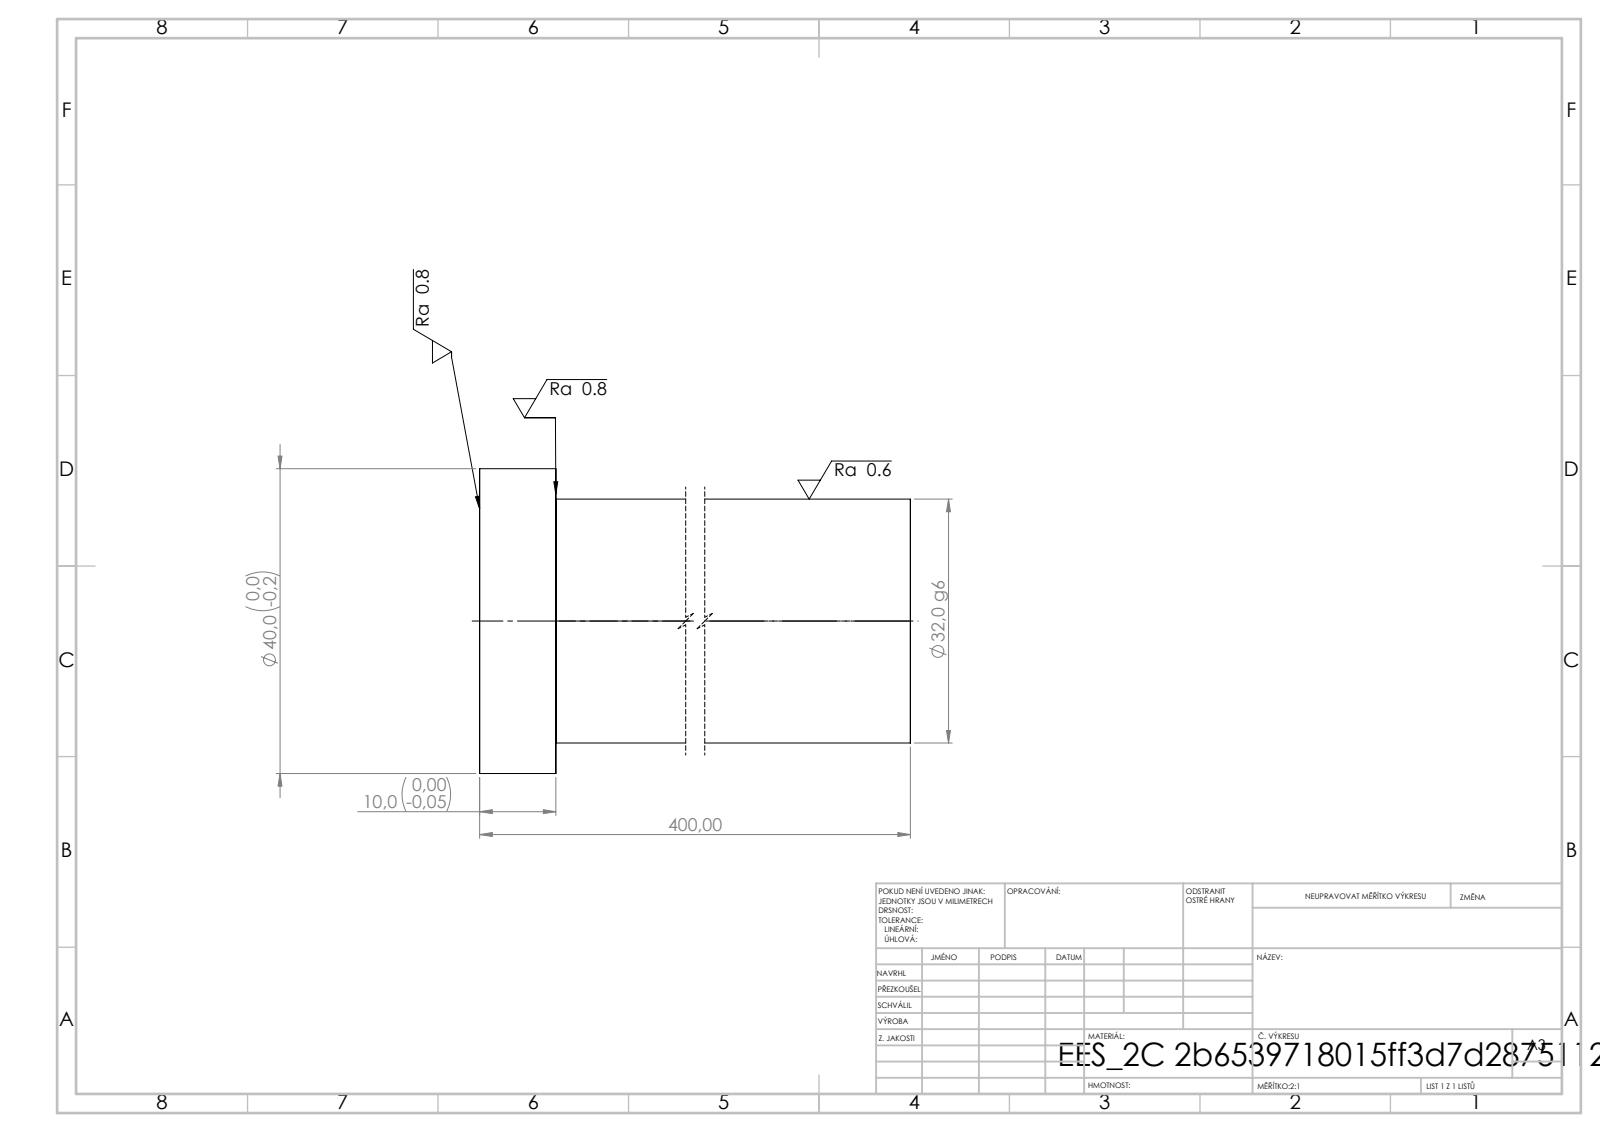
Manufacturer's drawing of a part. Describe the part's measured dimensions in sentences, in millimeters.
Its 3-D file was written by "SolidWorks 2019 (CONFIG_CONTROL_DESIGN)". It is 1 solid with 7 faces: 3 planar, 4 cylindrical and 0 other. Overall it measures 400 by 40 by 40 millimeters. Its volume is 326 223 cubic millimeters and its surface area 42 977 square millimeters. Round bosses or shafts: 1 of diameter 40, 1 of diameter 32. The main face-to-face distances are 400, 10, 390.
